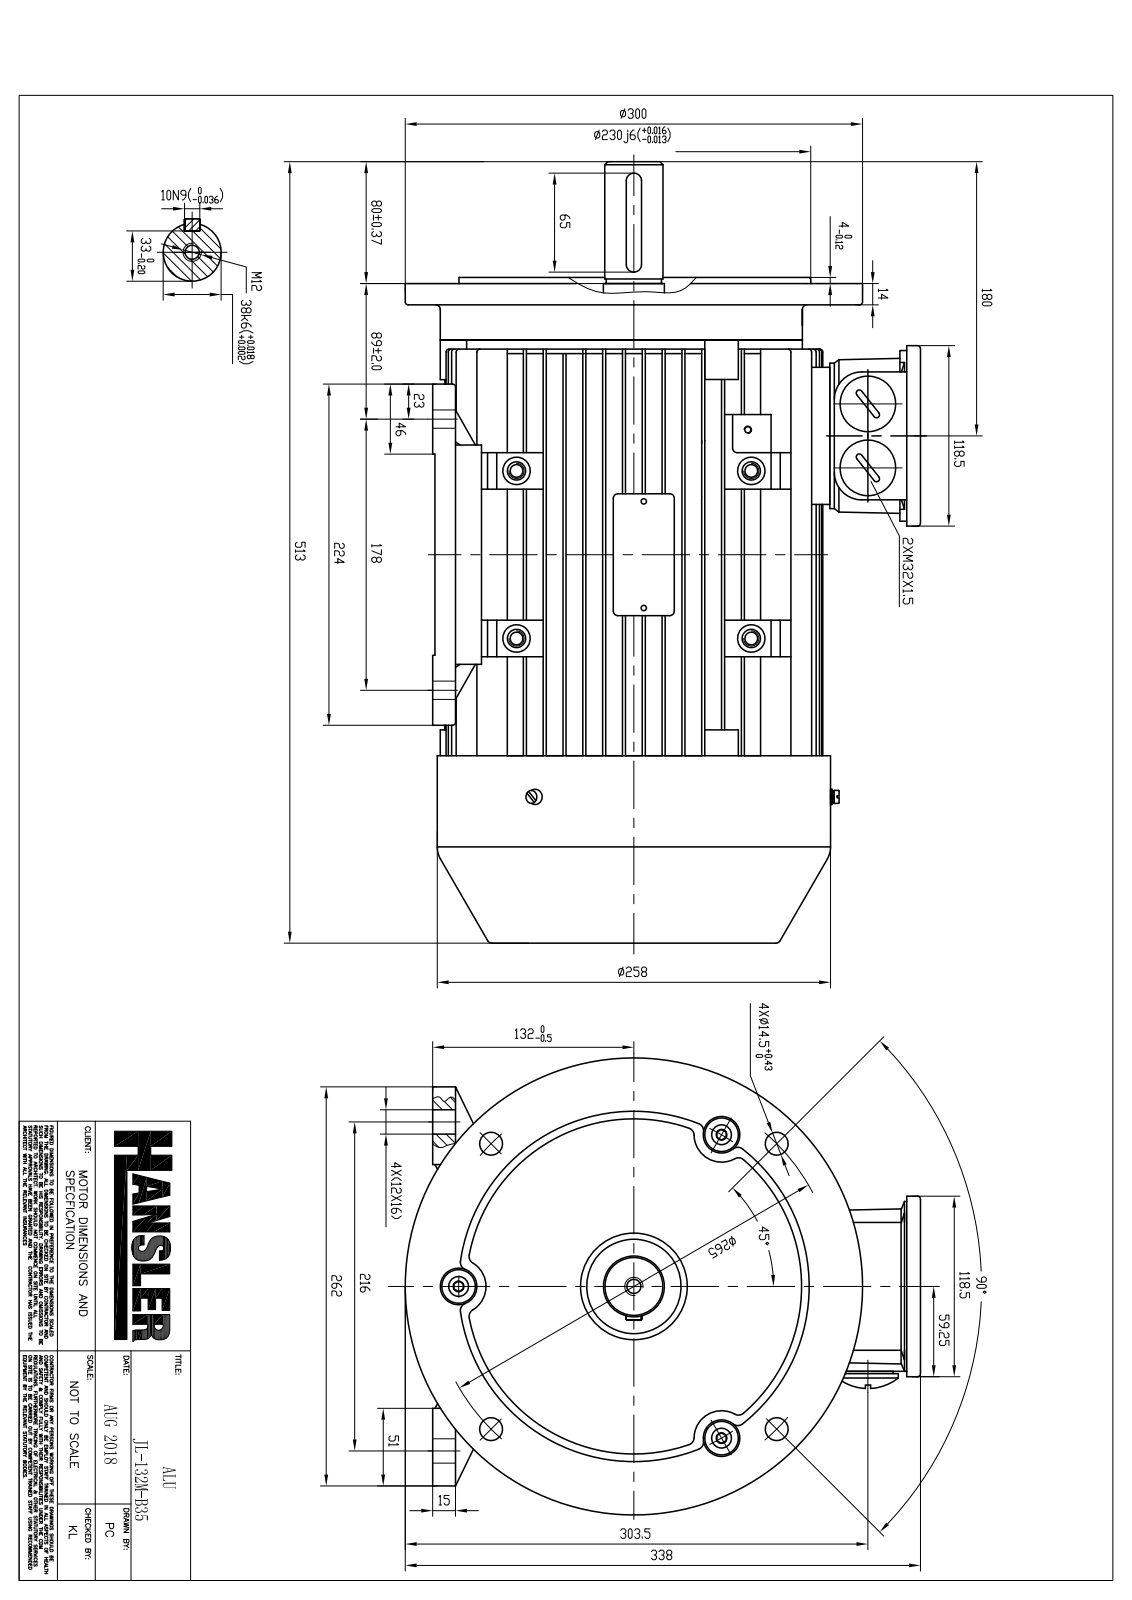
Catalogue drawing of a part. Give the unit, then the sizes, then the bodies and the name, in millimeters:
Units: millimetres
Overall size (bounding box): 513 × 341 × 300
Round holes (diameter × count): ⌀5 ×26, ⌀10 ×14, ⌀5.8 ×10, ⌀18 ×8, ⌀11 ×6, ⌀4.8 ×4, ⌀5.25 ×4, ⌀5.3 ×4, ⌀8 ×4, ⌀10.71 ×4, ⌀13 ×4, ⌀15 ×4
Round bosses / shafts (diameter × count): ⌀16 ×8, ⌀12 ×8, ⌀4.48 ×8, ⌀4.8 ×6, ⌀17.79 ×4, ⌀17 ×4, ⌀10 ×4, ⌀7.85 ×4
Partial cylindrical surfaces — rounded edges, fillets, slot ends (radius × count): R0.5 ×816, R2 ×130, R5 ×45, R3 ×34, R1 ×26, R4 ×26, R6 ×20, R2.5 ×18
Main face-to-face distances: 13, 2, 26, 11, 91, 104, 15, 78, 24, 117
Hole centre spacings: 40.23, 57.6, 61.1, 78.63, 84.34, 56.94, 144.72, 17.68
Volume: 4 042 000 mm³ · Surface area: 1 982 000 mm²
Bodies: 57 solids, 5476 faces (3268 planar, 1785 cylindrical, 423 other)
Part name (STEP PRODUCT): JL-132M-B35
STEP written by: SIEMENS PLM Software NX 12.0 (AP203_CONFIGURATION_CONTROLLED_3D_DESIGN_OF_MECHANICAL_PARTS_AND_ASSEMBLIES_MIM_LF)
